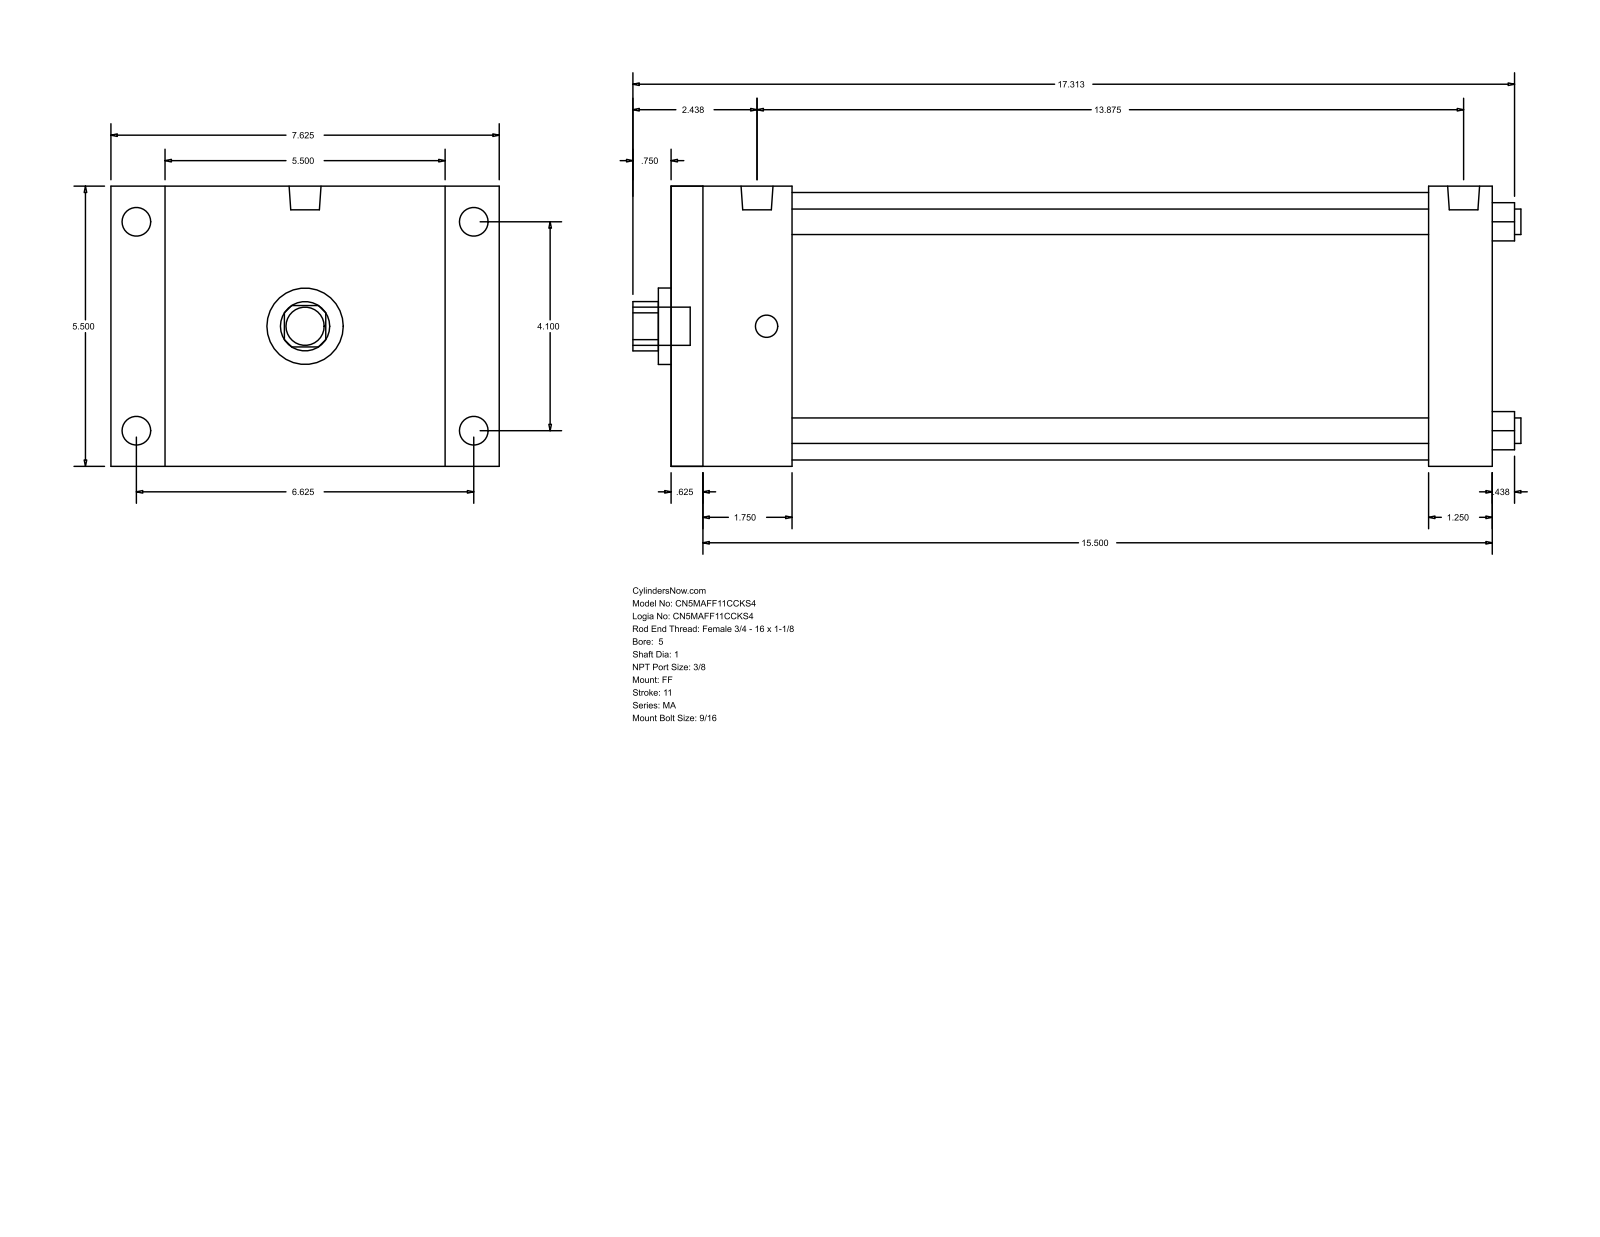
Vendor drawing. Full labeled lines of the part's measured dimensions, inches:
Part name (STEP PRODUCT): MA_FF__0500_1
STEP written by: GSSL Pune (CONFIG_CONTROL_DESIGN)
Units: inches
Bodies: 0 solids, 92 faces (64 planar, 28 cylindrical, 0 other)
Overall size (bounding box): 17.437 × 7.625 × 5.5
Round holes (diameter × count): ⌀0.5 ×4, ⌀1 ×1, ⌀1.5 ×1, ⌀5.25 ×1
Round bosses / shafts (diameter × count): ⌀0.563 ×4, ⌀0.437 ×4, ⌀0.627 ×2, ⌀0.75 ×1
Partial cylindrical surfaces — rounded edges, fillets, slot ends (radius × count): R0.484 ×1
Main face-to-face distances: 5.5, 16.125, 0.625, 15.5, 14.875, 14.25, 1.25, 2.375, 1.75, 12.5
Hole centre spacings: 2.899, 4.1, 5.798
